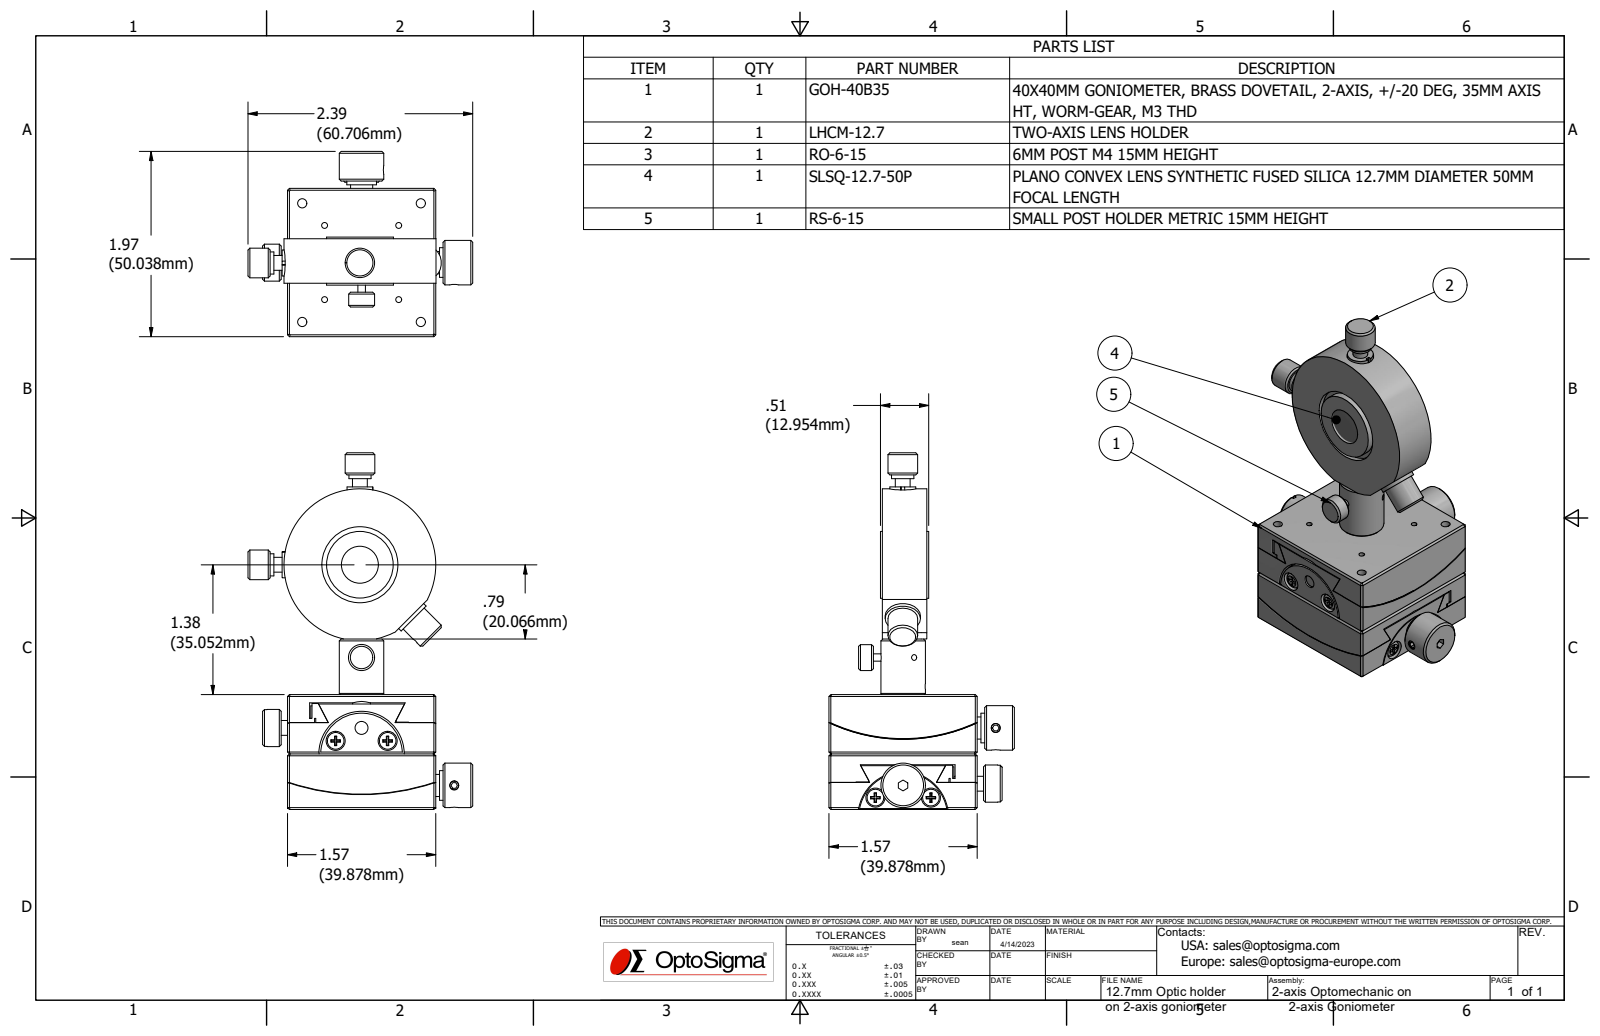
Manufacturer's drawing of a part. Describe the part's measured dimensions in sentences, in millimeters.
The part is named "Optomechanic on 2-axis Goni; GOH-40B35; LHCM-12.7 (no rod); RO-6-15 (+2 more)". Its 3-D file was written by "Autodesk Inventor 2022 (AUTOMOTIVE_DESIGN)". It is 20 solids with 1052 faces: 561 planar, 295 cylindrical and 196 other. Overall it measures 96.23 by 60.66 by 50 millimeters. Its volume is 64 788 cubic millimeters and its surface area 36 536 square millimeters. Round holes: 12 of diameter 1.57, 8 of diameter 2.46, 6 of diameter 2, 5 of diameter 6, 4 of diameter 2.11, 4 of diameter 3.2, 4 of diameter 3.5, 4 of diameter 5.2, 3 of diameter 1.57, 3 of diameter 1.6, 3 of diameter 2.11, 2 of diameter 3.24. Round bosses or shafts: 8 of diameter 3, 6 of diameter 4.5, 5 of diameter 8, 5 of diameter 4, 4 of diameter 6, 4 of diameter 3.5, 4 of diameter 2.6, 3 of diameter 12. Partial cylindrical surfaces (rounded edges, fillets, slot ends): 16 of radius 1.4, 12 of radius 0.7, 8 of radius 0.5, 4 of radius 3.5, 1 of radius 1.62, 1 of radius 3.46, 1 of radius 3.46, 1 of radius 11. The main face-to-face distances are 40, 31, 12, 25.59, 14.41, 26.41, 13.59, 1.5, 10.5, 0.5. The hole center spacings are 26.68, 18.36, 8.49, 14.14, 18.03, 20, 22.63, 25.
